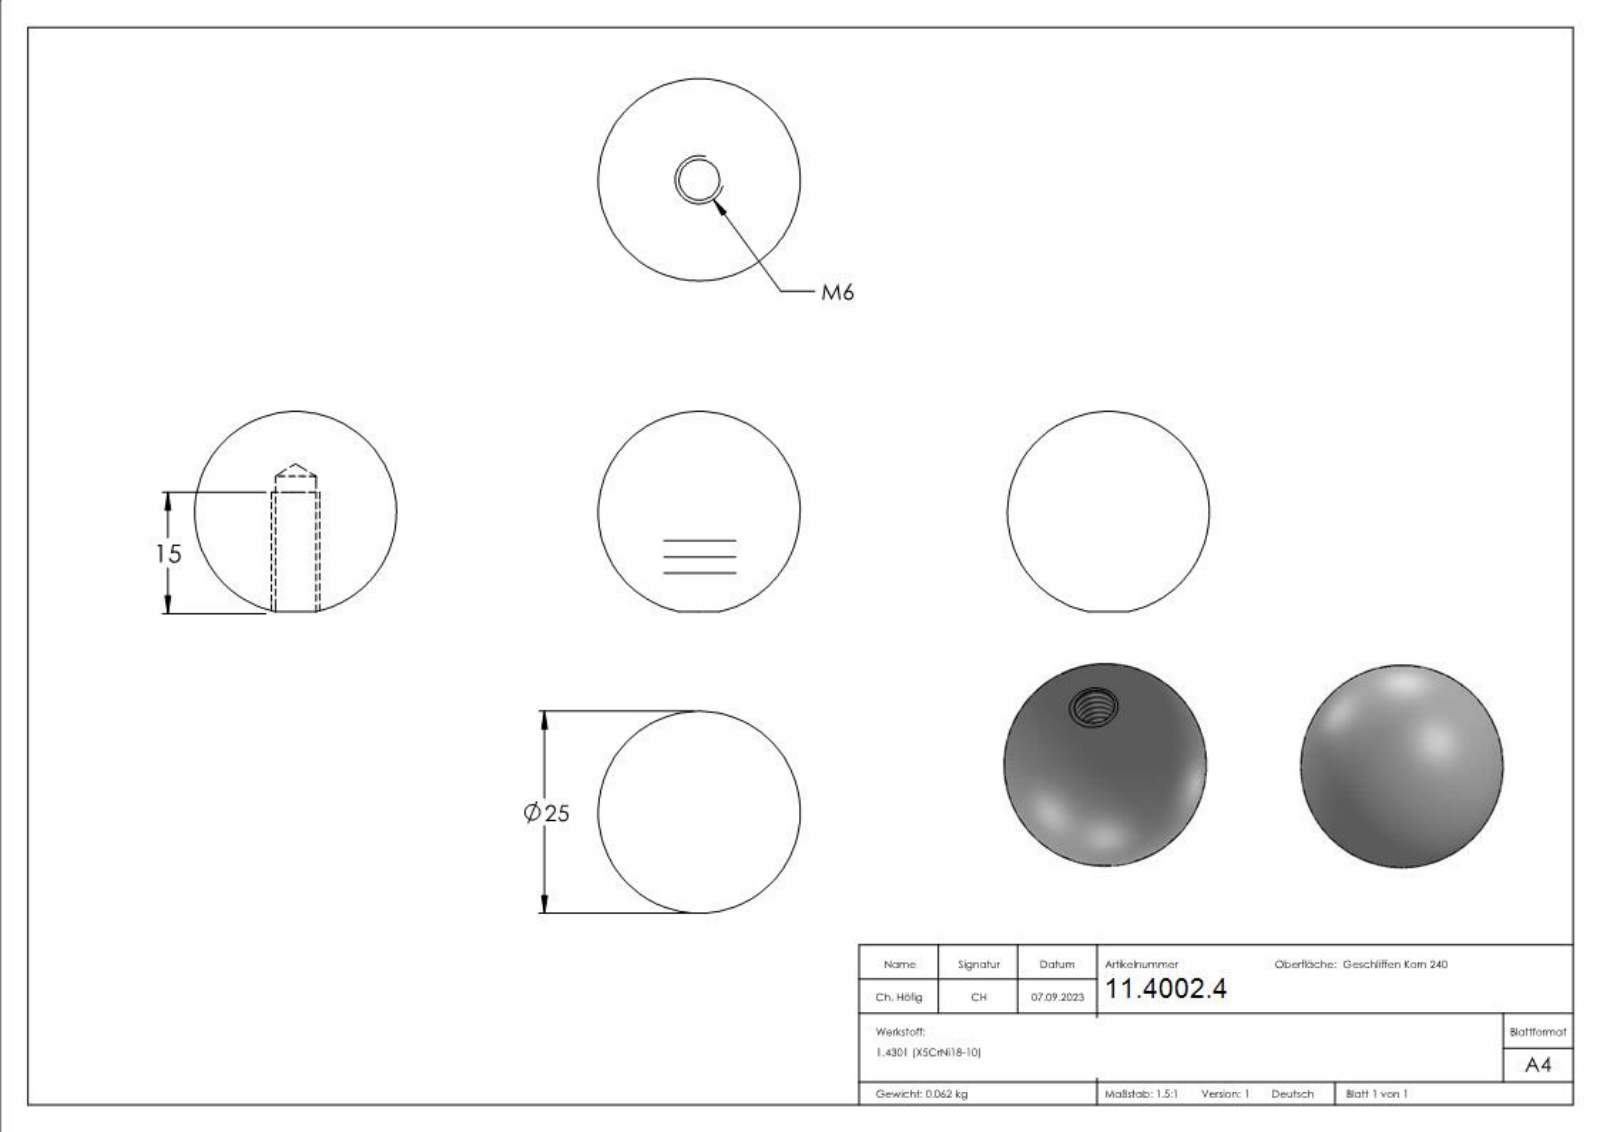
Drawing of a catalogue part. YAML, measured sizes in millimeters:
part_name: "51025-240"
step_written_by: "SolidWorks 2018 (CONFIG_CONTROL_DESIGN)"
units: millimeters
bodies: {solids: 1, faces: 3, planar: 0, cylindrical: 1, other: 2}
overall_size: [25, 25, 24.75]
volume: 7840
surface_area: 2230
round_holes:
  - {diameter: 5, count: 1}
